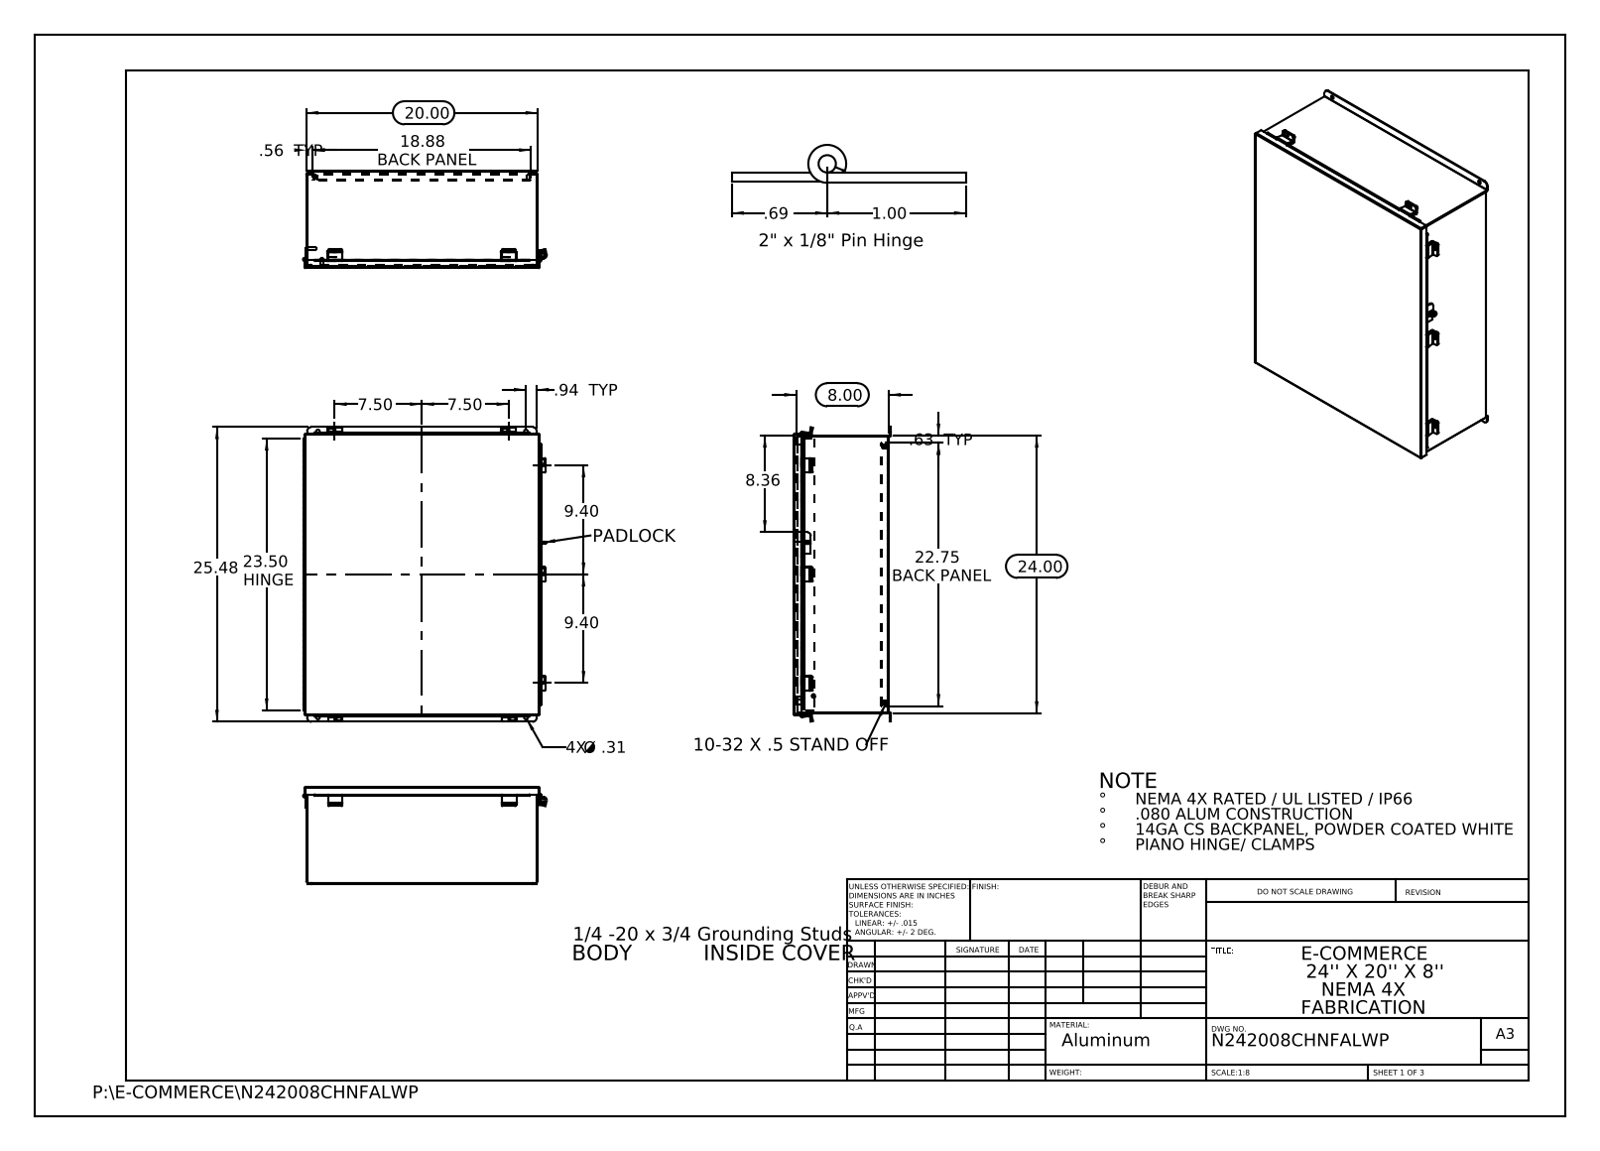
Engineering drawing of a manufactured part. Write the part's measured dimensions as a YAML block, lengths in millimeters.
part_name: "N242008CHNFALWP JIC_Standoff; N242008CHNFALWP JIC_Cover_Template; HW-CLH-JH-20154; N242008CHNFALWP _JIC Hinge (+8 more)"
step_written_by: "SolidWorks 2013 (CONFIG_CONTROL_DESIGN)"
units: millimeters
bodies: {solids: 29, faces: 1056, planar: 651, cylindrical: 385, other: 20}
overall_size: [647.1, 535.2, 213.1]
volume: 2802000
surface_area: 2986000
round_holes:
  - {diameter: 6.4, count: 11}
  - {diameter: 4.7, count: 4}
  - {diameter: 7.9, count: 4}
  - {diameter: 3.2, count: 1}
  - {diameter: 3.2, count: 1}
  - {diameter: 9.5, count: 1}
  - {diameter: 9.5, count: 1}
round_bosses_or_shafts:
  - {diameter: 8, count: 4}
  - {diameter: 8, count: 2}
  - {diameter: 6, count: 2}
  - {diameter: 6.9, count: 1}
  - {diameter: 6.4, count: 1}
partial_cylinders:
  - {radius: 3.2, count: 26}
  - {radius: 3.4, count: 14}
  - {radius: 0.3, count: 13}
  - {radius: 0.2, count: 12}
  - {radius: 2.2, count: 12}
  - {radius: 2.1, count: 6}
  - {radius: 2.5, count: 6}
  - {radius: 9.5, count: 4}
face_to_face_distances: [1.9, 206.5, 204.5, 208.4, 193.8, 14.6, 12.7, 191.8, 16.5, 14.6]
hole_center_spacings: [33.4, 462.8, 595, 753.1, 239.4, 381, 456.6, 466.7]
